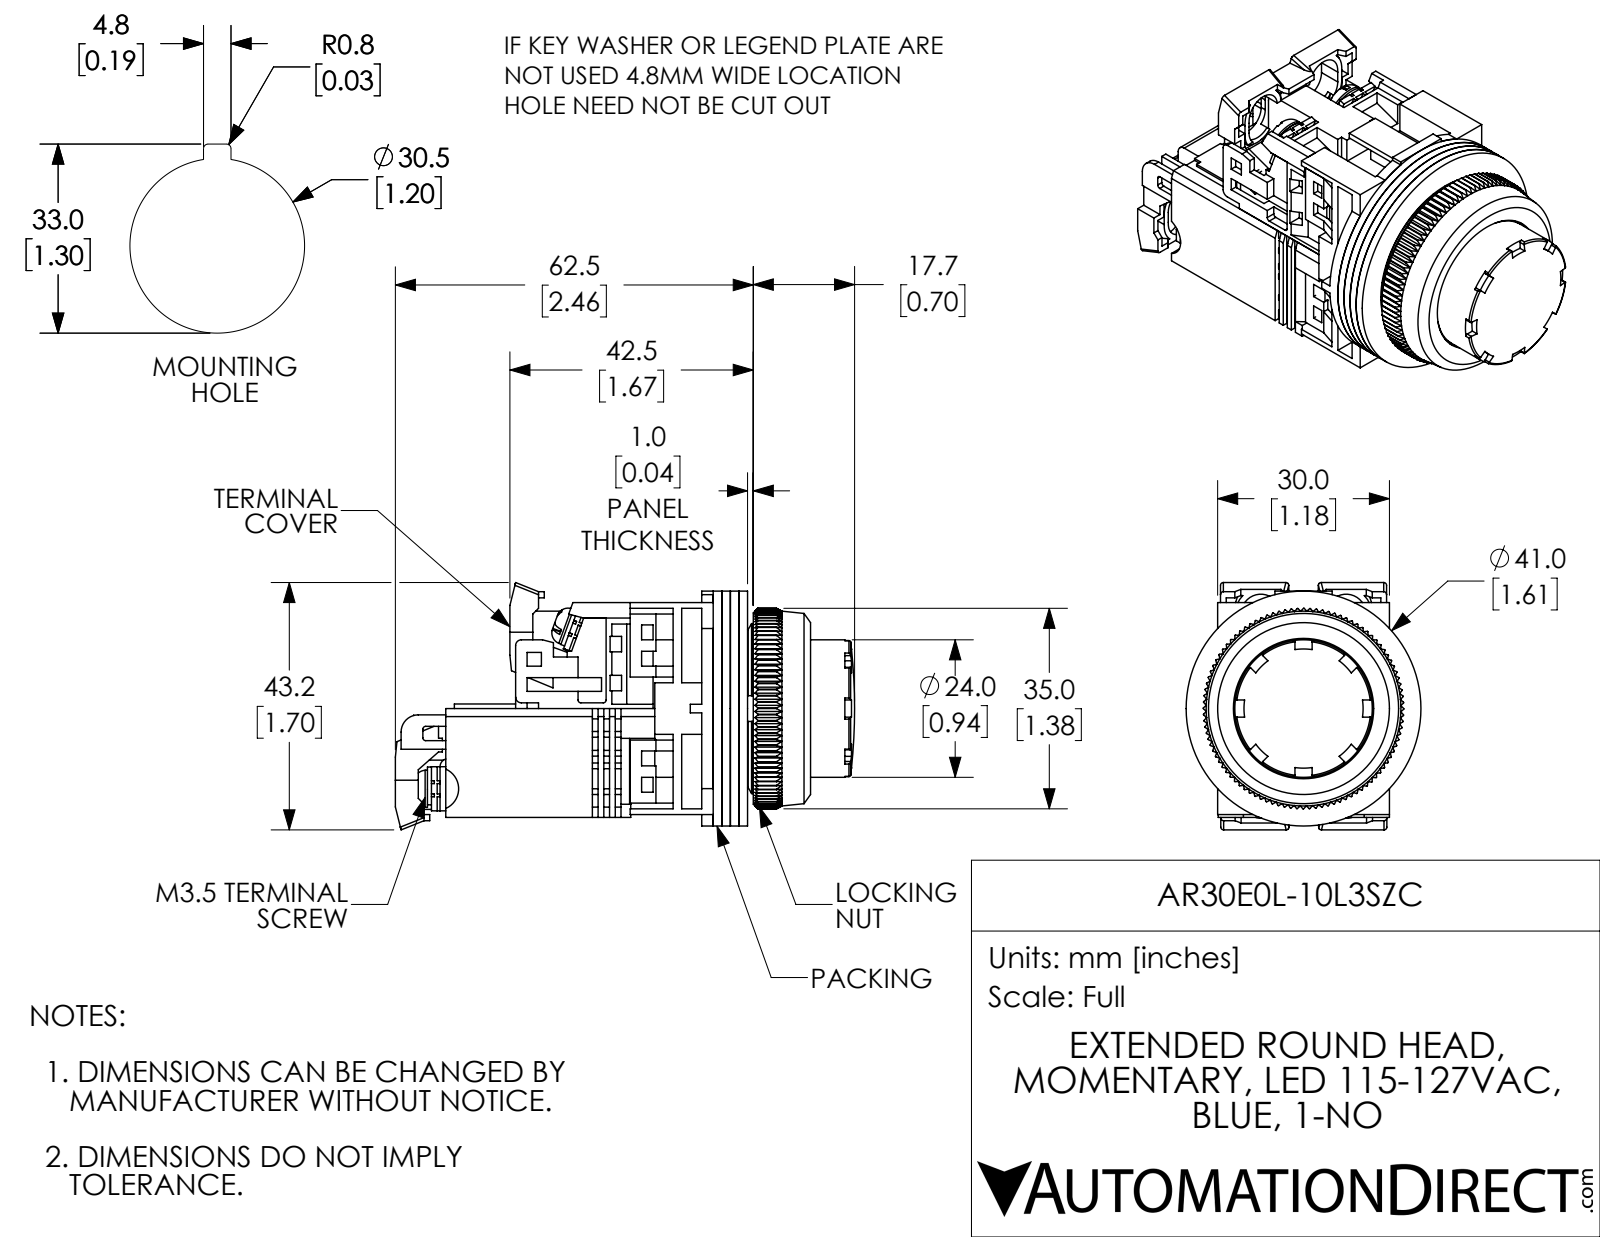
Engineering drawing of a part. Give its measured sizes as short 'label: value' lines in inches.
name: AR30E0L-10L3SZC
written by: SolidWorks 2017 (AUTOMOTIVE_DESIGN)
unit: in
bodies: 27 solids, 1960 faces (1368 planar, 339 cylindrical, 253 other)
size: 3.157 × 1.7 × 1.614
volume: 2.883 in³; area: 64.03 in²
holes: 6× ⌀0.138, 4× ⌀0.142, 3× ⌀0.118, 1× ⌀0.472, 1× ⌀0.709, 1× ⌀0.728, 1× ⌀0.787, 1× ⌀0.945, 1× ⌀0.965, 1× ⌀1.122, 1× ⌀1.252
bosses: 4× ⌀0.26, 2× ⌀0.138, 1× ⌀1.614, 1× ⌀1.181, 1× ⌀0.866, 1× ⌀0.776, 1× ⌀0.551
rounds: 17× R0.059, 16× R0.012, 13× R0.02, 4× R0.138, 4× R0.177, 2× R0.039, 2× R0.118, 1× R0.016
face distances: 0.059, 0.118, 0.177, 0.748, 0.039, 0.02, 0.079, 1.417, 0.689, 0.047
hole spacings: 0.579, 0.02, 0.295, 0.299, 0.3, 0.583, 0.583, 0.605
